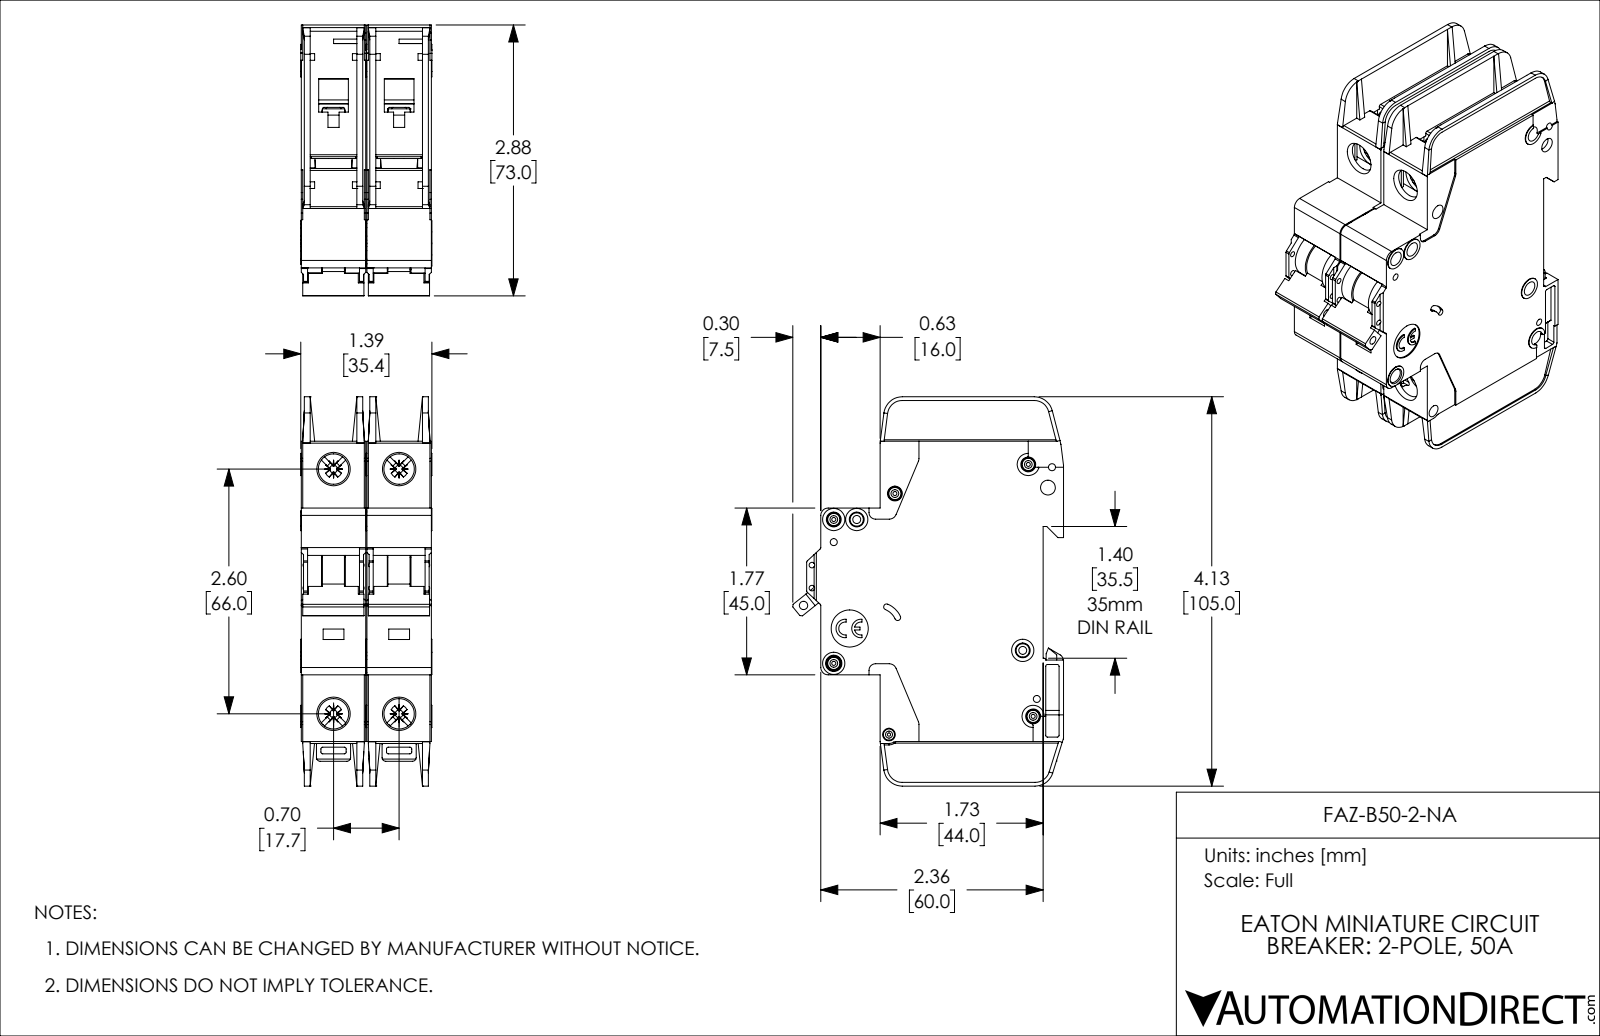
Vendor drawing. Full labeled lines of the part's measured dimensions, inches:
Part name (STEP PRODUCT): FAZ-B50-2-NA
STEP written by: SolidWorks 2019 (AUTOMOTIVE_DESIGN)
Units: inches
Bodies: 2 solids, 2254 faces (1342 planar, 714 cylindrical, 198 other)
Overall size (bounding box): 4.134 × 2.876 × 1.394
Volume: 9.365 in³ · Surface area: 82.01 in²
Round holes (diameter × count): ⌀0.157 ×8, ⌀0.043 ×5, ⌀0.075 ×4, ⌀0.323 ×4, ⌀0.059 ×2, ⌀0.085 ×2, ⌀0.035 ×1, ⌀0.089 ×1, ⌀0.098 ×1, ⌀0.134 ×1, ⌀0.394 ×1
Round bosses / shafts (diameter × count): ⌀0.13 ×5, ⌀0.236 ×4, ⌀0.118 ×3, ⌀0.098 ×2
Partial cylindrical surfaces — rounded edges, fillets, slot ends (radius × count): R0.02 ×57, R0.016 ×20, R0.039 ×14, R0.079 ×10, R0.043 ×8, R0.008 ×5, R0.197 ×5, R0.01 ×4
Main face-to-face distances: 0.697, 0.047, 0.685, 0.591, 0.094, 0.638, 0.543, 1.382, 0.744, 0.65
Hole centre spacings: 0.244, 0.537, 0.697, 0.87, 2.598, 2.69, 0.189, 0.199
